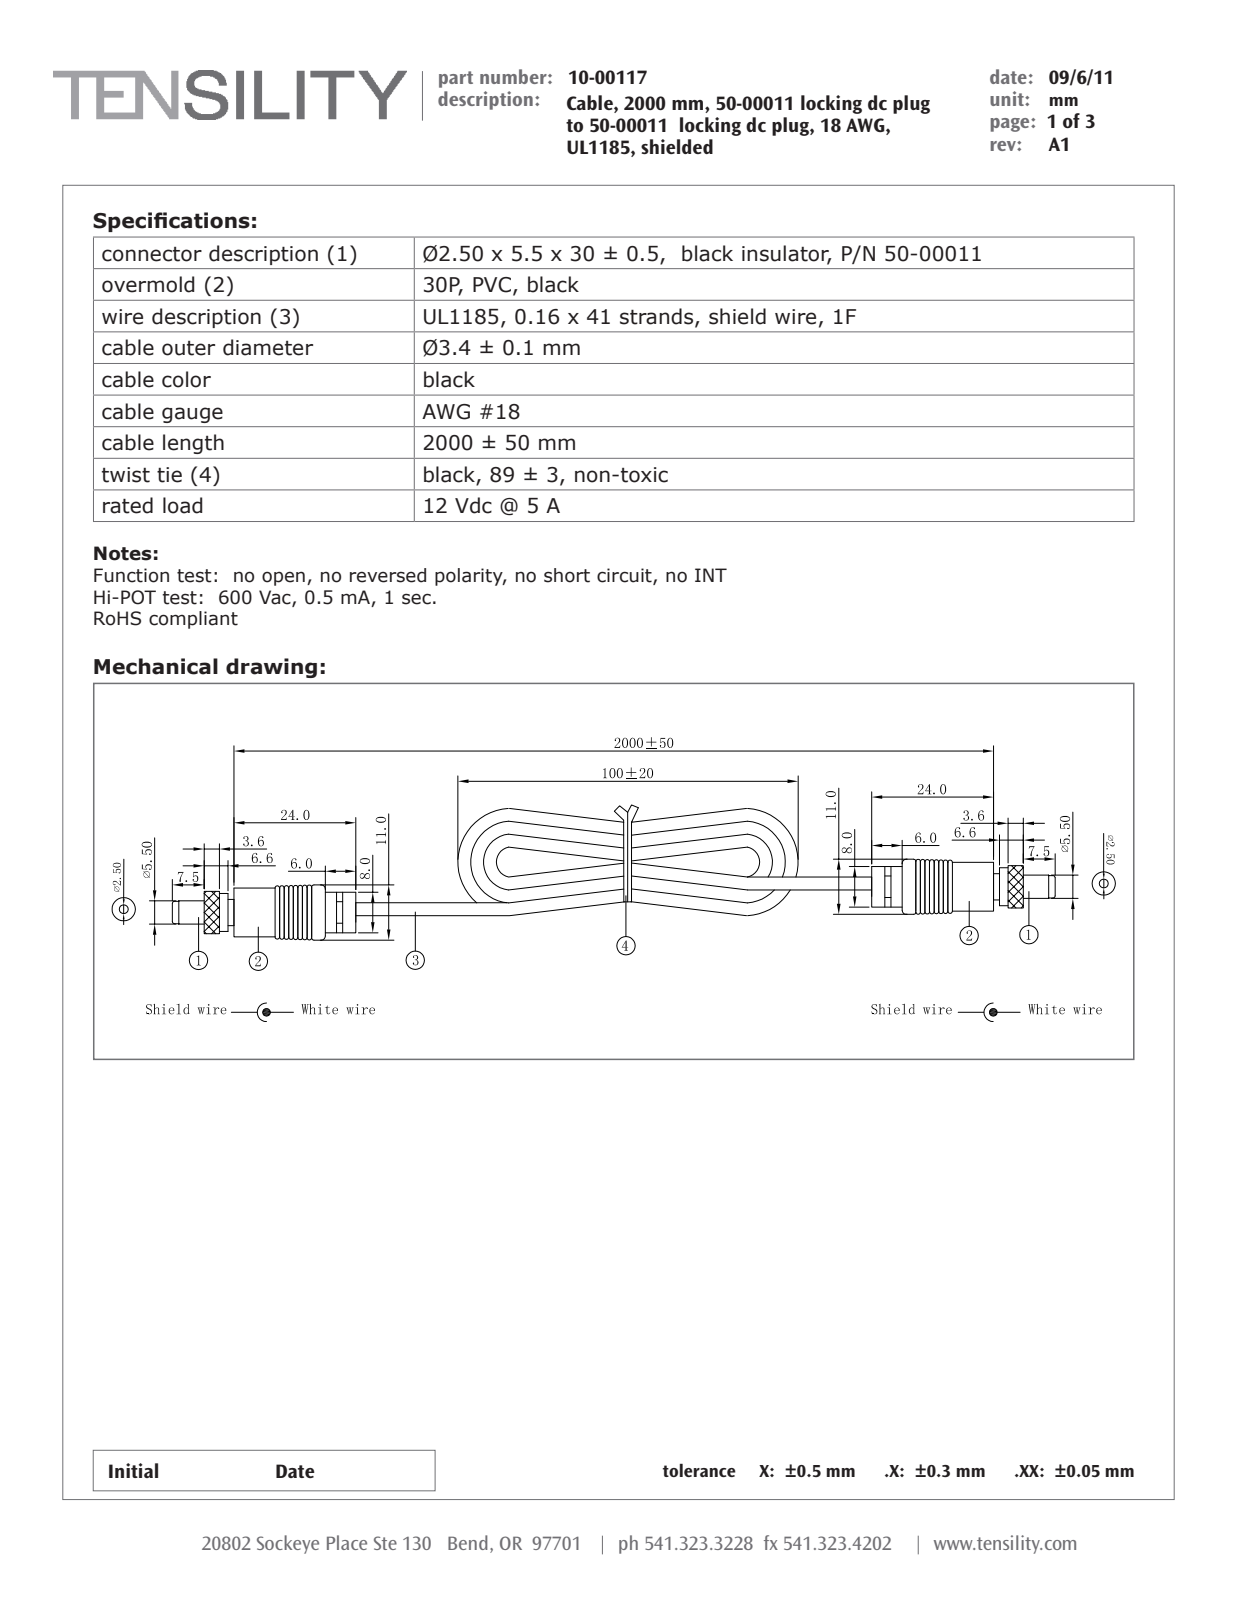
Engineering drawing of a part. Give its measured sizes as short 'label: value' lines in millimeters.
name: 24-00016; 50-00011 shell 2; 10-00117; 50-00011 (+6 more)
written by: SolidWorks 2015 (CONFIG_CONTROL_DESIGN)
unit: mm
bodies: 98 solids, 2944 faces (862 planar, 642 cylindrical, 1440 other)
size: 221.6 × 11 × 11
volume: 6 150 mm³; area: 18 735 mm²
holes: 1× ⌀1.26, 1× ⌀1.6, 1× ⌀2.16, 1× ⌀2.4, 1× ⌀2.5, 1× ⌀3, 1× ⌀3.25, 1× ⌀4.25, 1× ⌀5.04, 1× ⌀5.44, 1× ⌀5.5, 1× ⌀5.65
bosses: 1× ⌀11, 1× ⌀10, 1× ⌀8, 1× ⌀7, 1× ⌀6.2, 1× ⌀6, 1× ⌀5.48, 1× ⌀5.3
rounds: 12× R0.2, 4× R0.55, 1× R3.92
face distances: 24, 165.8, 19.9, 169.9, 4.1, 145.9, 13.4, 21.4, 168.4, 1.5
